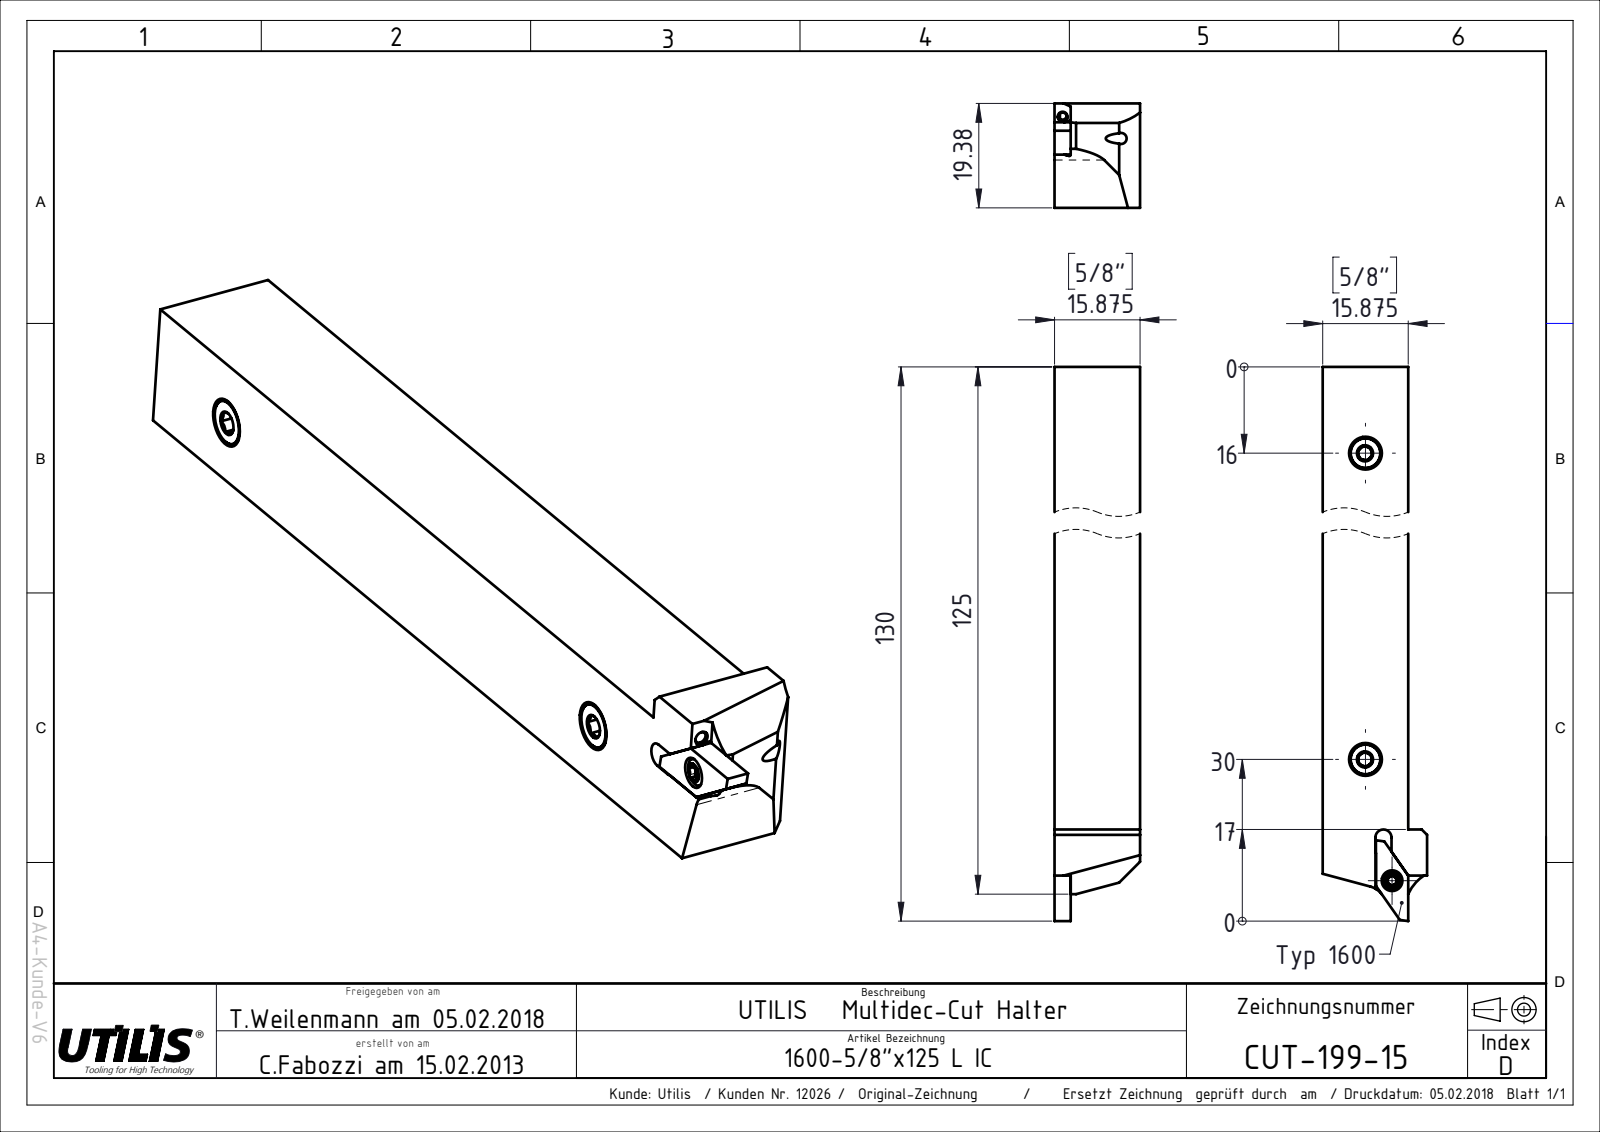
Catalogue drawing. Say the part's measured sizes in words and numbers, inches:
The part is named "CUT-199-15". Its 3-D file was written by "SolidWorks 2017 (AUTOMOTIVE_DESIGN)". It is 1 solid with 39 faces: 30 planar, 6 cylindrical and 3 other. Overall it measures 5.118 by 0.763 by 0.625 inches. Its volume is 1.899 cubic inches and its surface area 13.13 square inches. Partial cylindrical surfaces (rounded edges, fillets, slot ends): 2 of radius 0.059, 1 of radius 0.01, 1 of radius 0.157. The main face-to-face distances are 0.625, 0.625, 0.763, 0.138, 4.449, 0.118, 0.236, 0.507, 0.389, 0.374.
